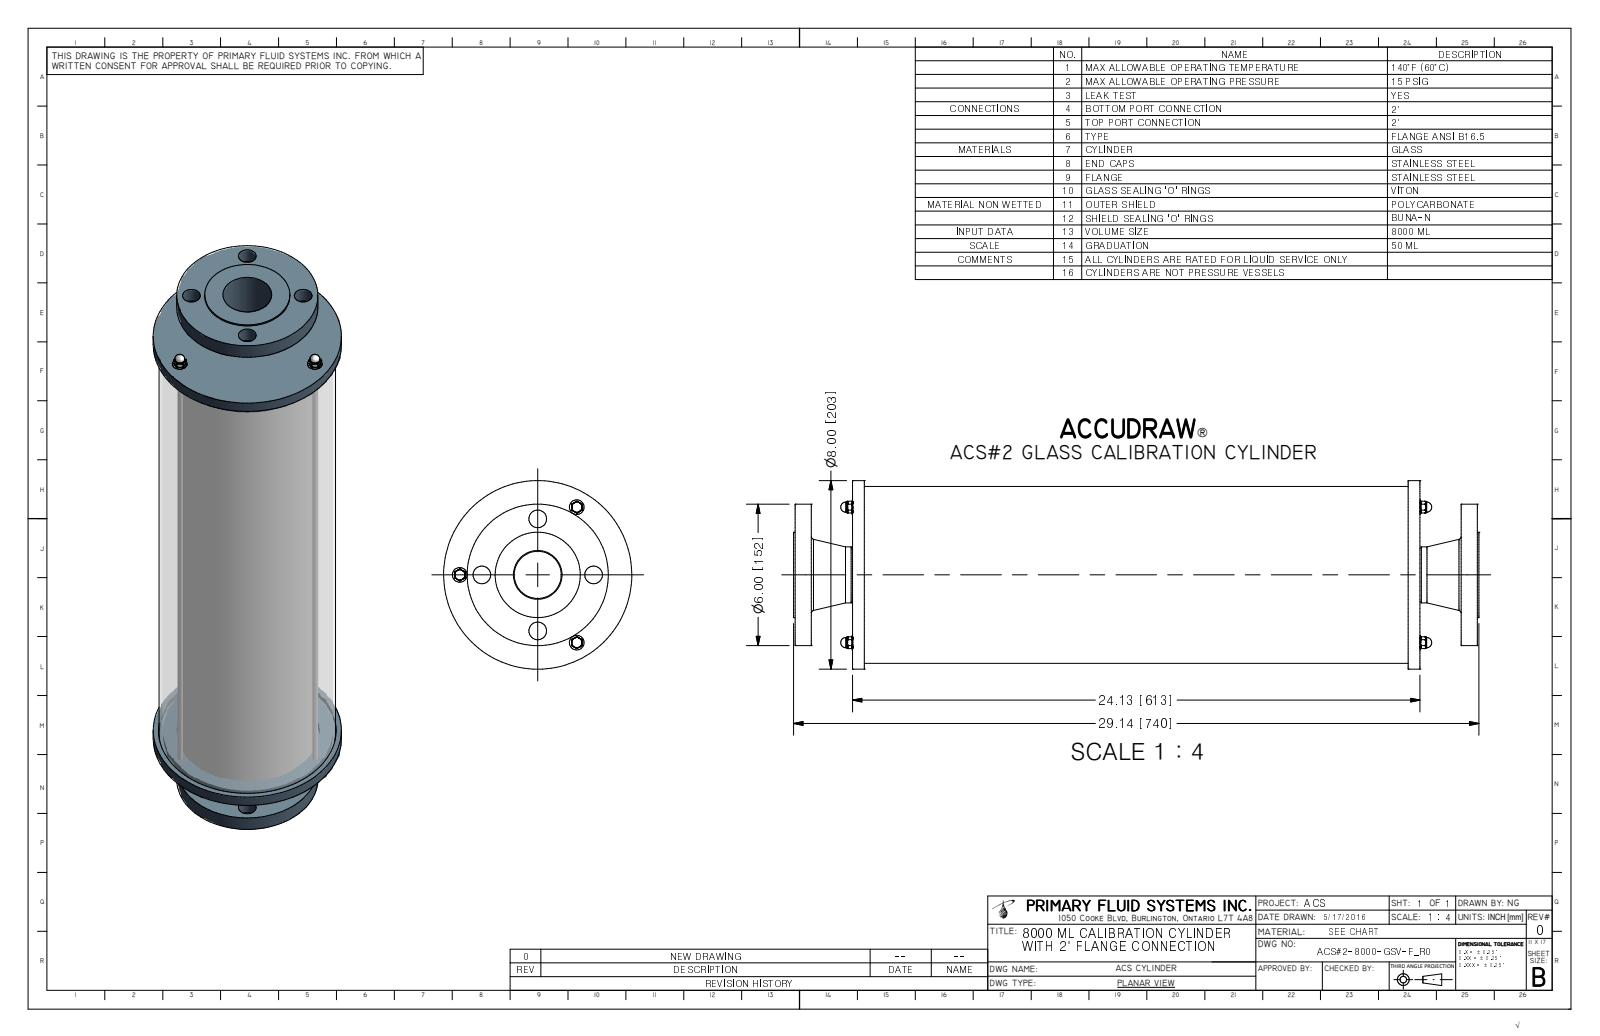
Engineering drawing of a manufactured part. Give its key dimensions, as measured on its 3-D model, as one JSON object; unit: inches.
{"part_name": "ACS#2-8000-GSV-F_R0; ACS-3-8000-METAL-S_R1; ACS-2-8000_R6; ACS-1-8000-A_R0 (+4 more)", "step_written_by": "Autodesk Inventor 2009 (AUTOMOTIVE_DESIGN)", "units": "inches", "bodies": {"solids": 21, "faces": 455, "planar": 46, "cylindrical": 57, "other": 352}, "overall_size": [29.135, 8, 8], "volume_in3": 235.3, "surface_area_in2": 2478, "round_holes": [[0.75, 4], [0.18, 3], [0.266, 3], [0.281, 3], [2.067, 1], [5.512, 1], [6.068, 1], [7.25, 1], [7.55, 1]], "round_bosses_or_shafts": [[0.625, 3], [0.25, 3], [8, 1], [7.5, 1], [7.2, 1], [6, 1], [5.906, 1], [5.427, 1]], "face_to_face_distances": [24.13, 1.75, 25.88, 2.25, 25.38, 0.5, 23.63, 0.69, 2.44, 2.94], "hole_center_spacings": [2.375, 3.359, 3.317, 1.731, 2.961, 4.08, 4.75, 4.952]}
